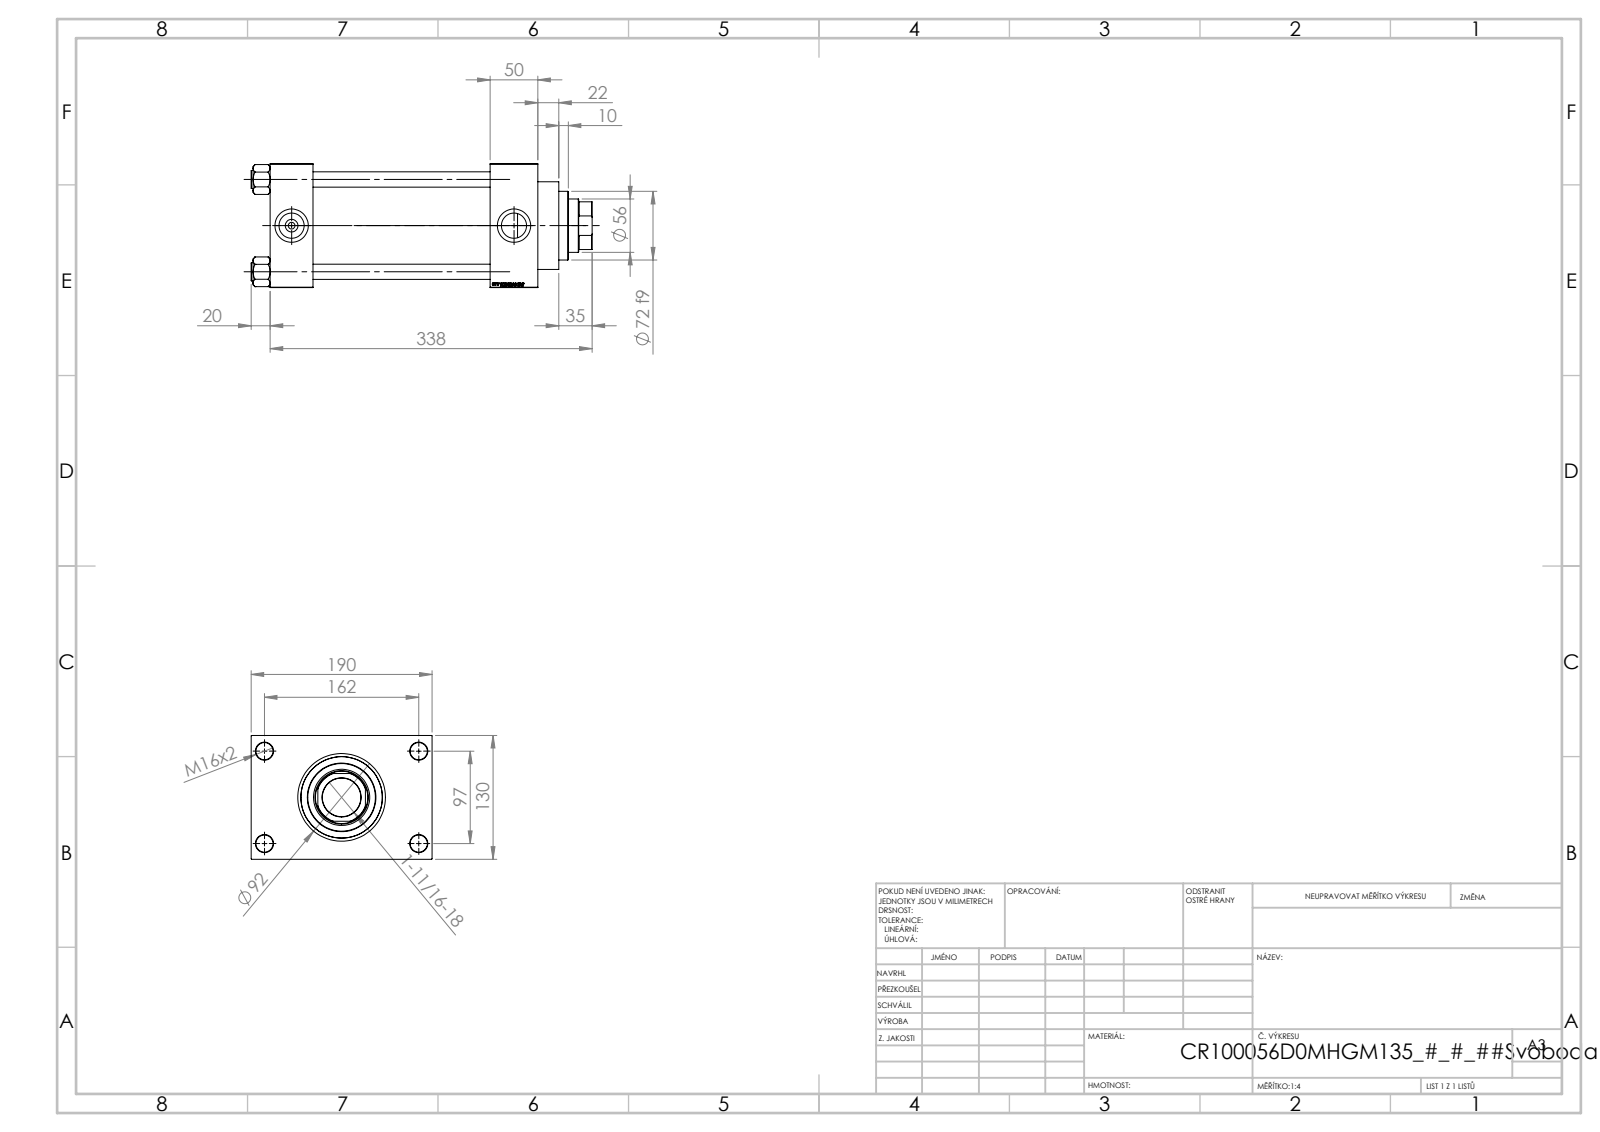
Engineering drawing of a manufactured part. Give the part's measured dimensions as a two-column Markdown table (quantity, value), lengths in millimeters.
| quantity | value |
| --- | --- |
| part name | V215CR_D_Body; V215_VC_A; V215CR_VCP_D; V215CR_D_TYCINKA (+1 more) |
| STEP written by | SolidWorks 2019 (CONFIG_CONTROL_DESIGN) |
| units | millimeters |
| bodies | 11 solids, 1151 faces (545 planar, 88 cylindrical, 518 other) |
| overall size | 358 × 190 × 130 |
| volume | 3 115 000 mm³ |
| surface area | 480 141 mm² |
| round holes (diameter × count) | 16 × 4, 18 × 4, 7 × 2, 26.44 × 2, 35 × 2, 40.5 × 1, 56 × 1, 59 × 1, 76 × 1, 85.5 × 1, 100 × 1 |
| round bosses / shafts (diameter × count) | 19 × 4, 106 × 1, 92 × 1, 72 × 1 |
| partial cylindrical surfaces (radius × count) | 27 × 1 |
| main face-to-face distances | 130, 50, 45, 186, 231, 281, 236, 30, 160, 190 |
| hole center spacings | 32.55, 68.52, 94.41, 96.9, 102.27, 129.45, 161.73, 97 |
